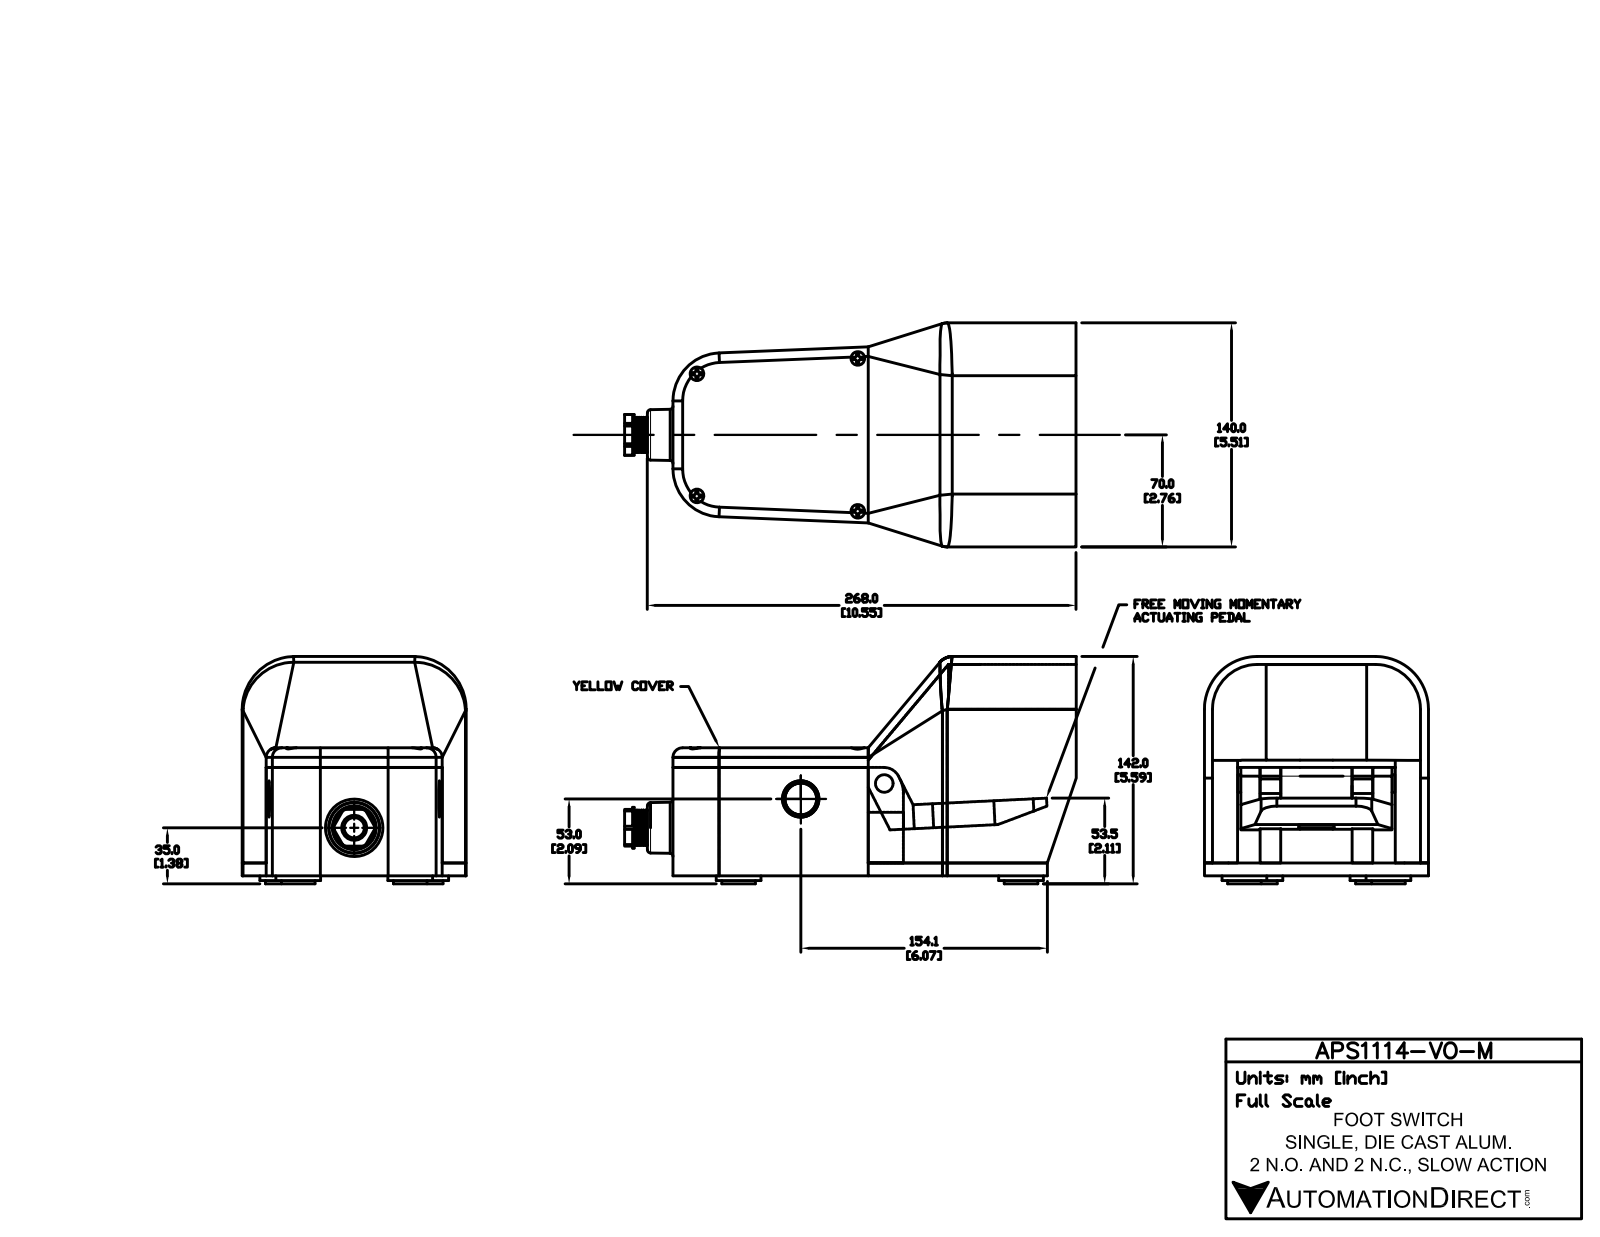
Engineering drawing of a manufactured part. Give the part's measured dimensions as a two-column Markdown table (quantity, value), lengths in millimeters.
| quantity | value |
| --- | --- |
| part name | APS1114-V0-M |
| STEP written by | SolidWorks 2015 (AUTOMOTIVE_DESIGN) |
| units | millimeters |
| bodies | 18 solids, 361 faces (214 planar, 91 cylindrical, 56 other) |
| overall size | 282.25 × 142 × 140 |
| volume | 1 541 000 mm³ |
| surface area | 267 977 mm² |
| round holes (diameter × count) | 8.5 × 4, 22.75 × 2, 12.65 × 1, 15.6 × 1 |
| round bosses / shafts (diameter × count) | 28 × 4, 21 × 4, 19.87 × 2, 25.5 × 1, 22 × 1, 11 × 1 |
| partial cylindrical surfaces (radius × count) | 1 × 16, 10 × 6, 5.99 × 3, 28 × 2, 30 × 2, 33 × 2, 20 × 1 |
| main face-to-face distances | 5, 135, 8, 59.64, 67.67, 59.67, 67.64, 140, 80, 72 |
| hole center spacings | 101, 132.24, 76.3, 95.5 |
